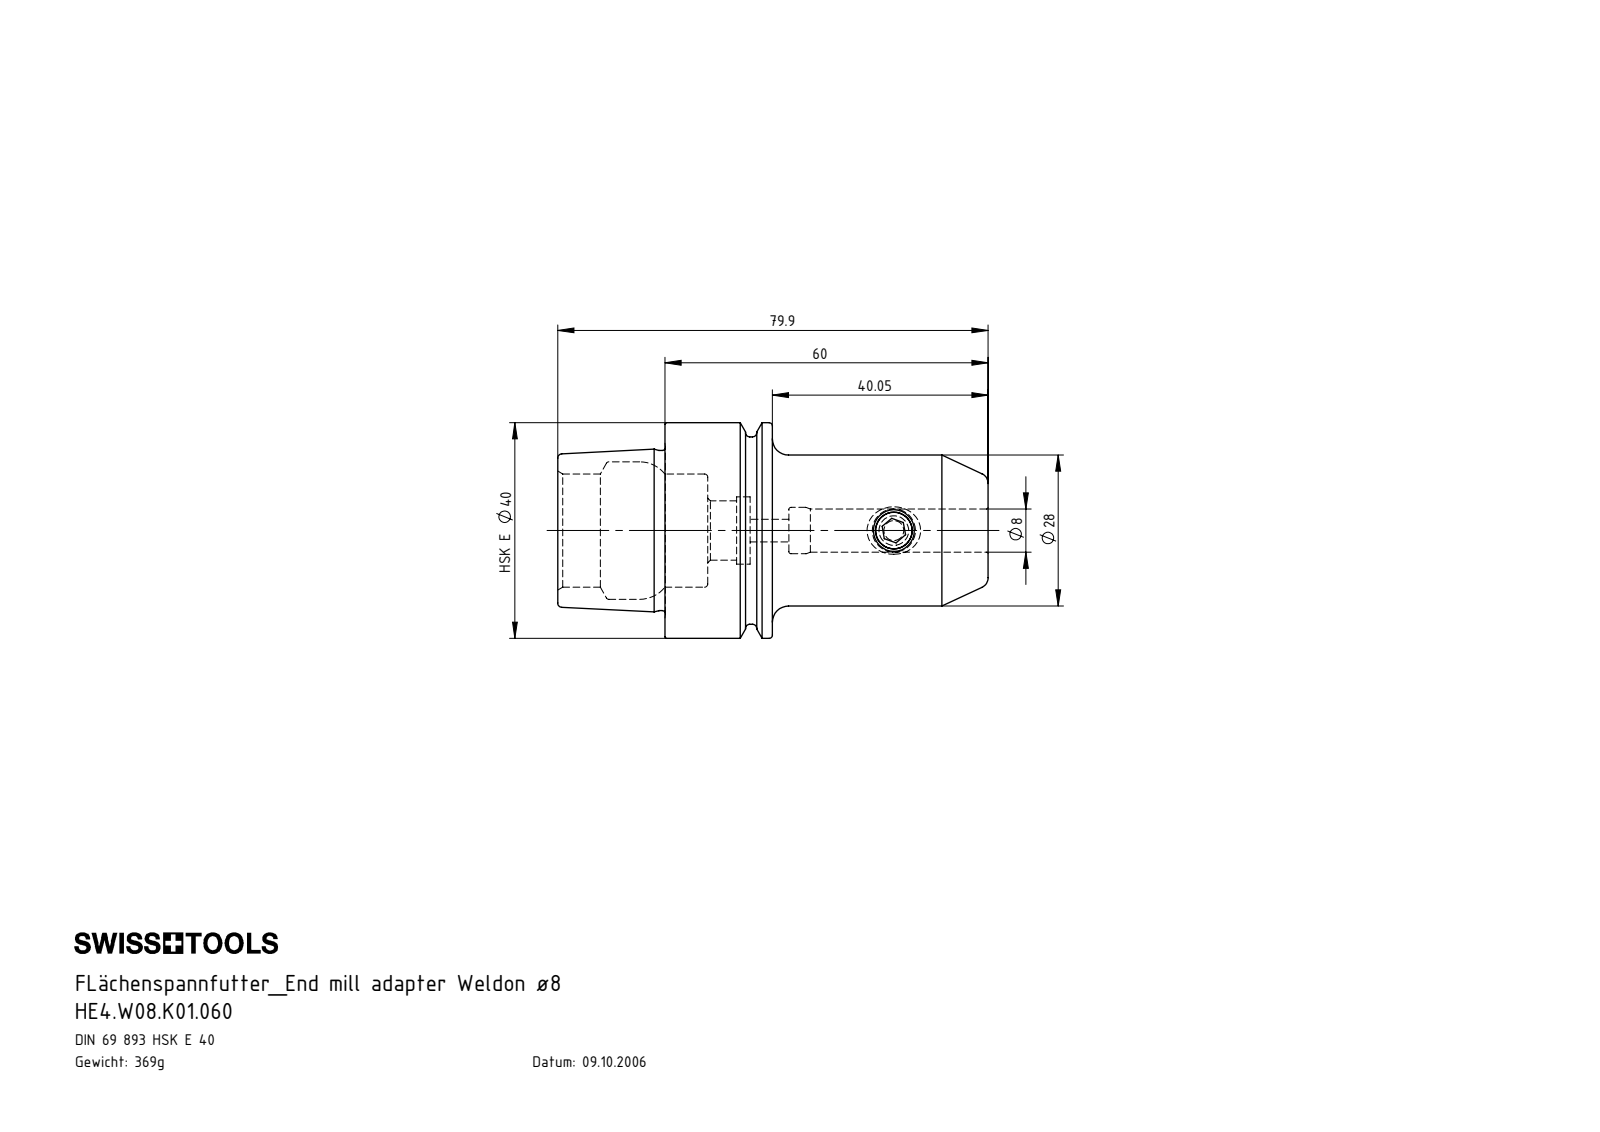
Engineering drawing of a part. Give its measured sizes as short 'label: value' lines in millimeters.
name: HE4.W08.K01.060; HE4-W08.K01.060_B_Fertigbearbeitung; W08-ER1.001.010
written by: SolidWorks 2017 (AUTOMOTIVE_DESIGN)
unit: mm
bodies: 2 solids, 64 faces (19 planar, 15 cylindrical, 30 other)
size: 79.9 × 40 × 40
volume: 47 030 mm³; area: 14 055 mm²
holes: 1× ⌀4.2, 1× ⌀6.8, 1× ⌀8, 1× ⌀8.6, 1× ⌀11, 1× ⌀12.5, 1× ⌀21, 1× ⌀25.5
bosses: 1× ⌀40, 1× ⌀34.75, 1× ⌀29.71, 1× ⌀28, 1× ⌀8
face distances: 19.95, 7.95, 12, 19.9, 27.85, 39.85, 79.9, 60, 52.05, 40.05
